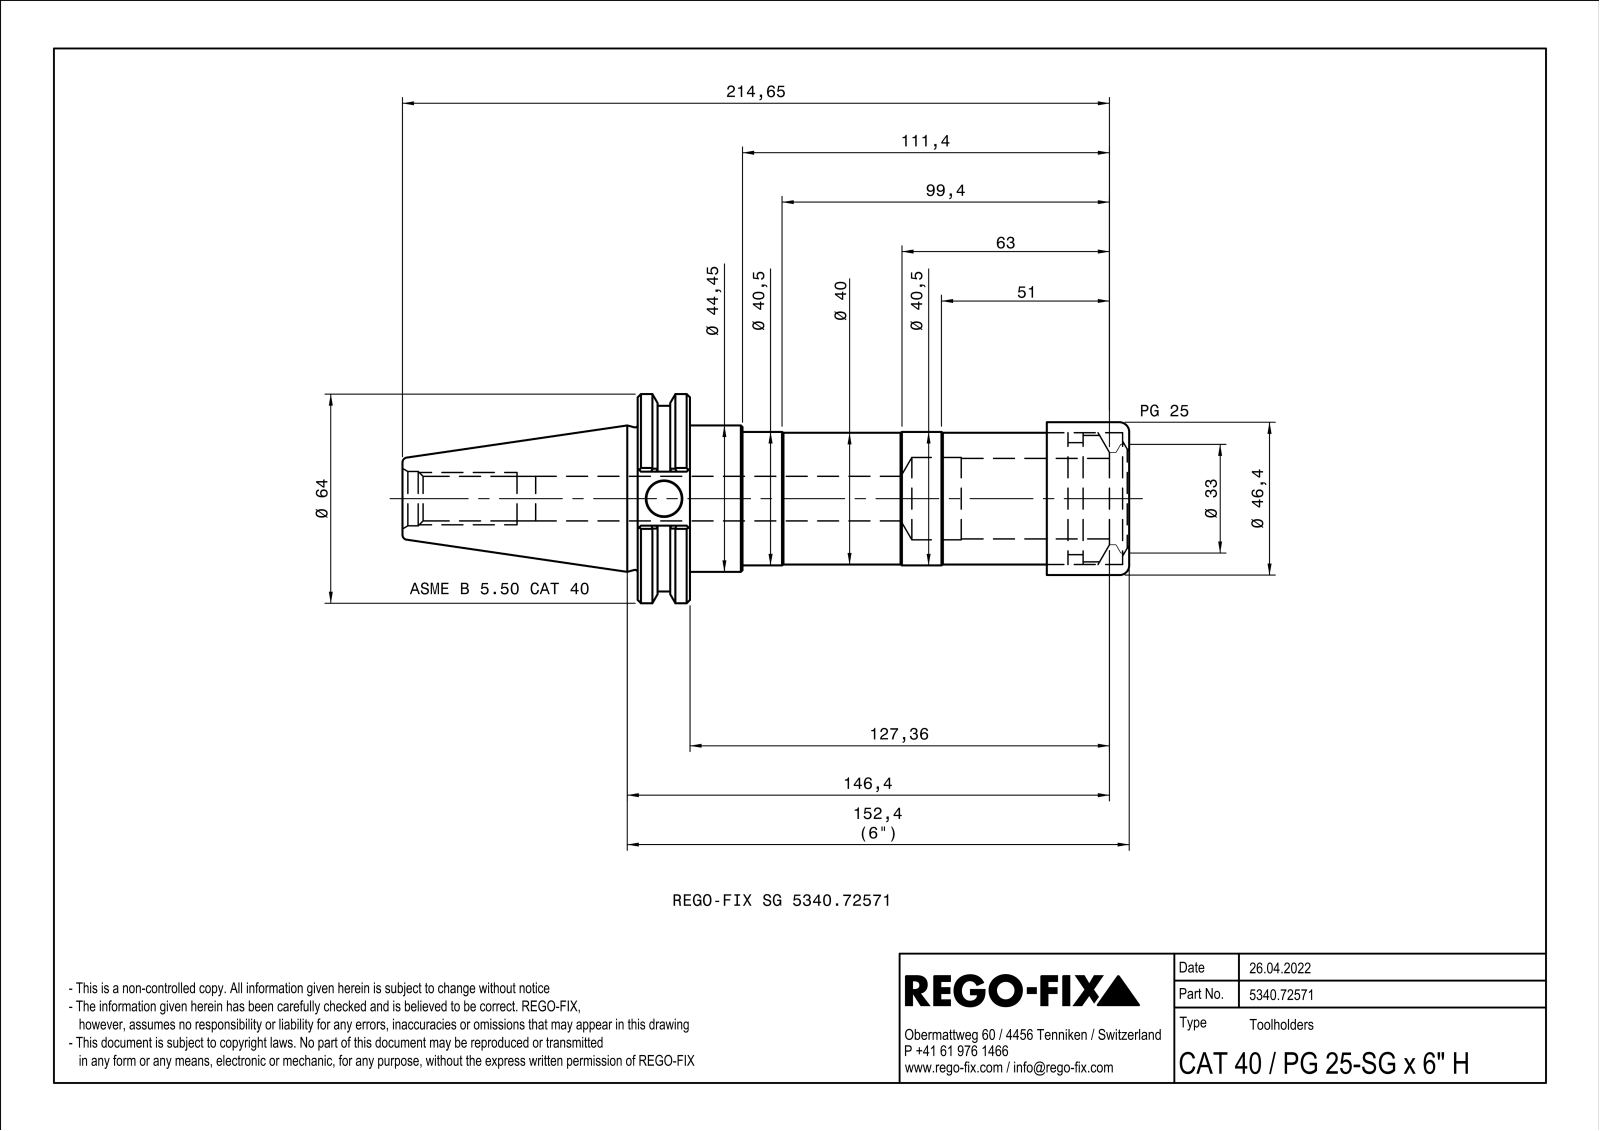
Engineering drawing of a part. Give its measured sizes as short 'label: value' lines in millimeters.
name: NOCUT
written by: SIEMENS PLM Software Solid Edge ST10 (AUTOMOTIVE_DESIGN)
unit: mm
bodies: 1 solid, 114 faces (37 planar, 25 cylindrical, 52 other)
size: 220.65 × 63.5 × 60.79
volume: 233 793 mm³; area: 51 131 mm²
holes: 1× ⌀10.7, 1× ⌀13.53, 1× ⌀16.5, 1× ⌀25, 1× ⌀30, 1× ⌀40.05, 1× ⌀42
bosses: 1× ⌀63.5, 1× ⌀56.36, 1× ⌀46.4, 1× ⌀46, 1× ⌀44.45, 1× ⌀40.5, 1× ⌀40, 1× ⌀34
rounds: 4× R0.5
face distances: 15.87, 133.36, 149.23, 25, 108.36, 124.23, 18.6, 6.4, 114.76, 130.63
